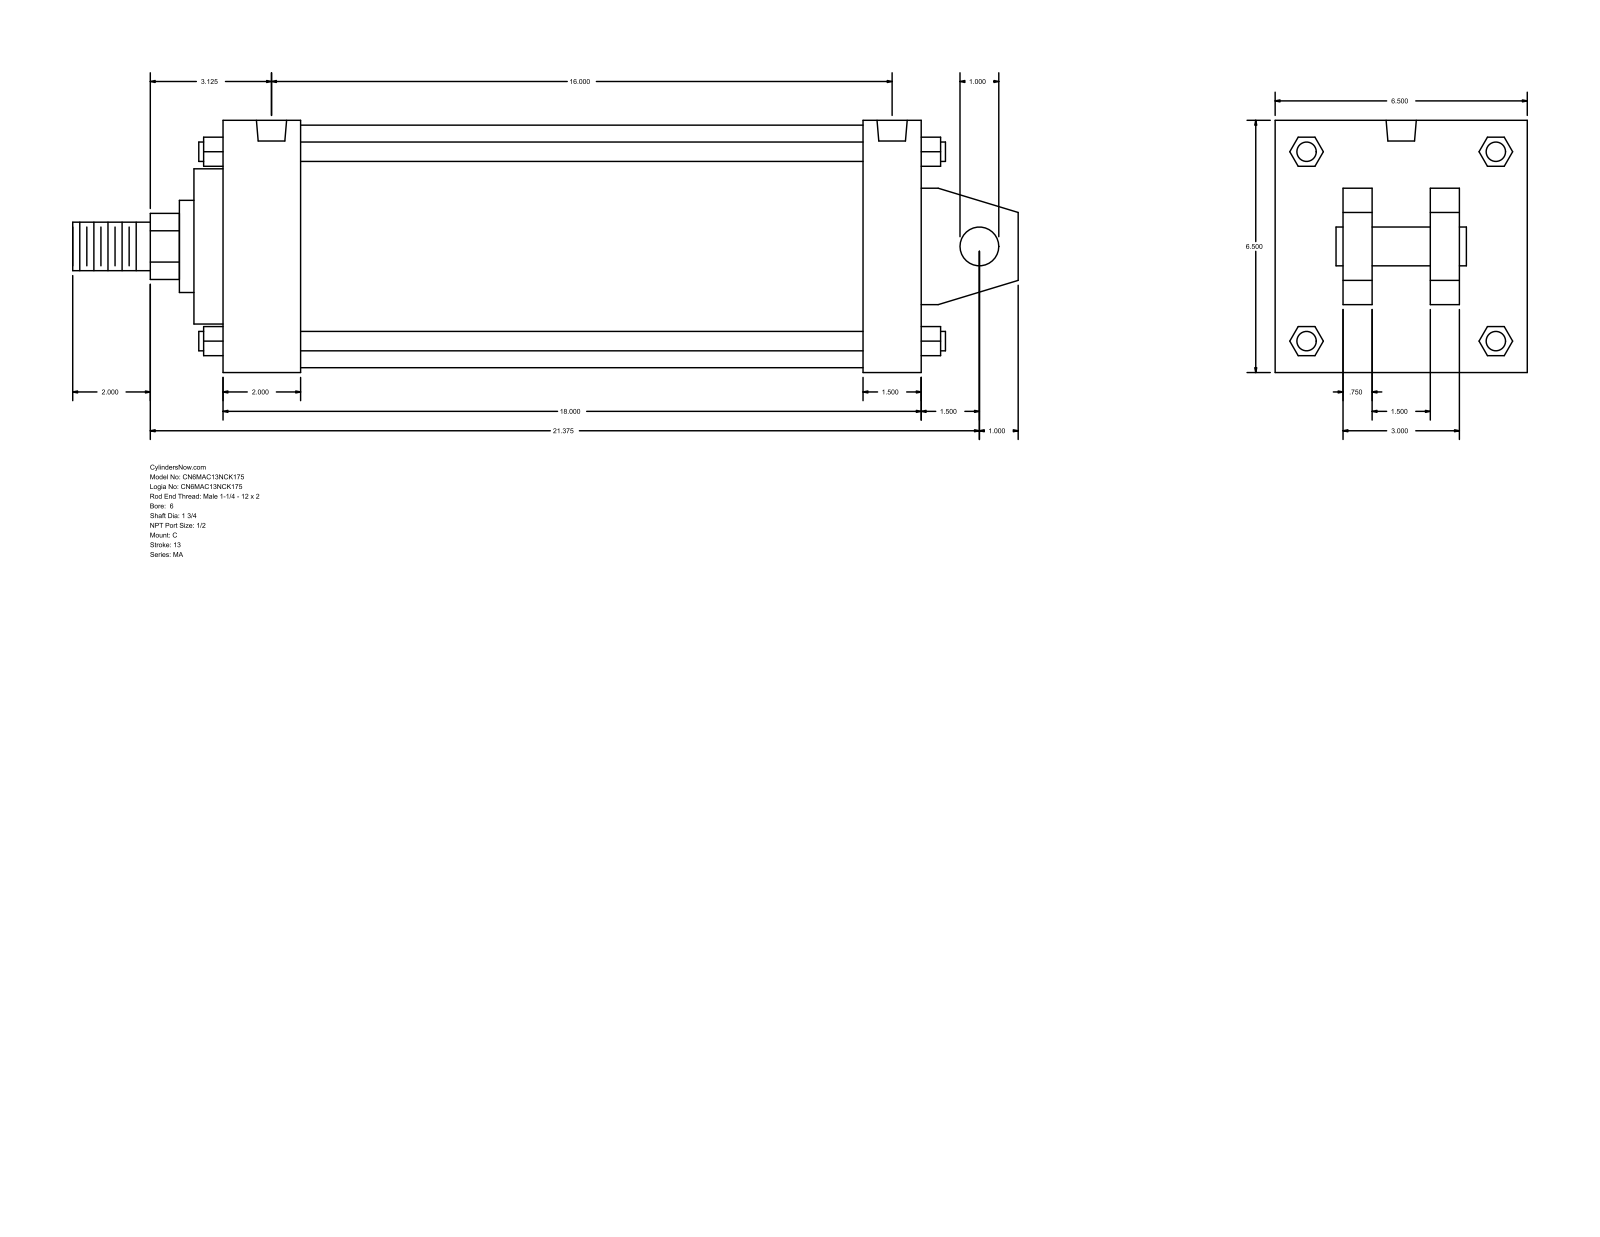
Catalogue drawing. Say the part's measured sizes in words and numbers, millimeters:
The part is named "MA_C__0600_1.75". Its 3-D file was written by "GSSL Pune (CONFIG_CONTROL_DESIGN)". It is 0 solids with 141 faces: 109 planar, 32 cylindrical and 0 other. Overall it measures 619.12 by 165.1 by 165.1 millimeters. Round holes: 4 of diameter 17.46, 2 of diameter 19.77. Round bosses or shafts: 4 of diameter 12.7, 1 of diameter 158.75, 1 of diameter 101.6, 1 of diameter 60.33, 1 of diameter 44.45, 1 of diameter 31.75, 1 of diameter 25.4. Partial cylindrical surfaces (rounded edges, fillets, slot ends): 1 of radius 21.63. The main face-to-face distances are 165.1, 457.2, 19.05, 101.6, 63.5, 44.45, 120.65, 57.15, 50.8, 406.4. The hole center spacings are 406.39.
